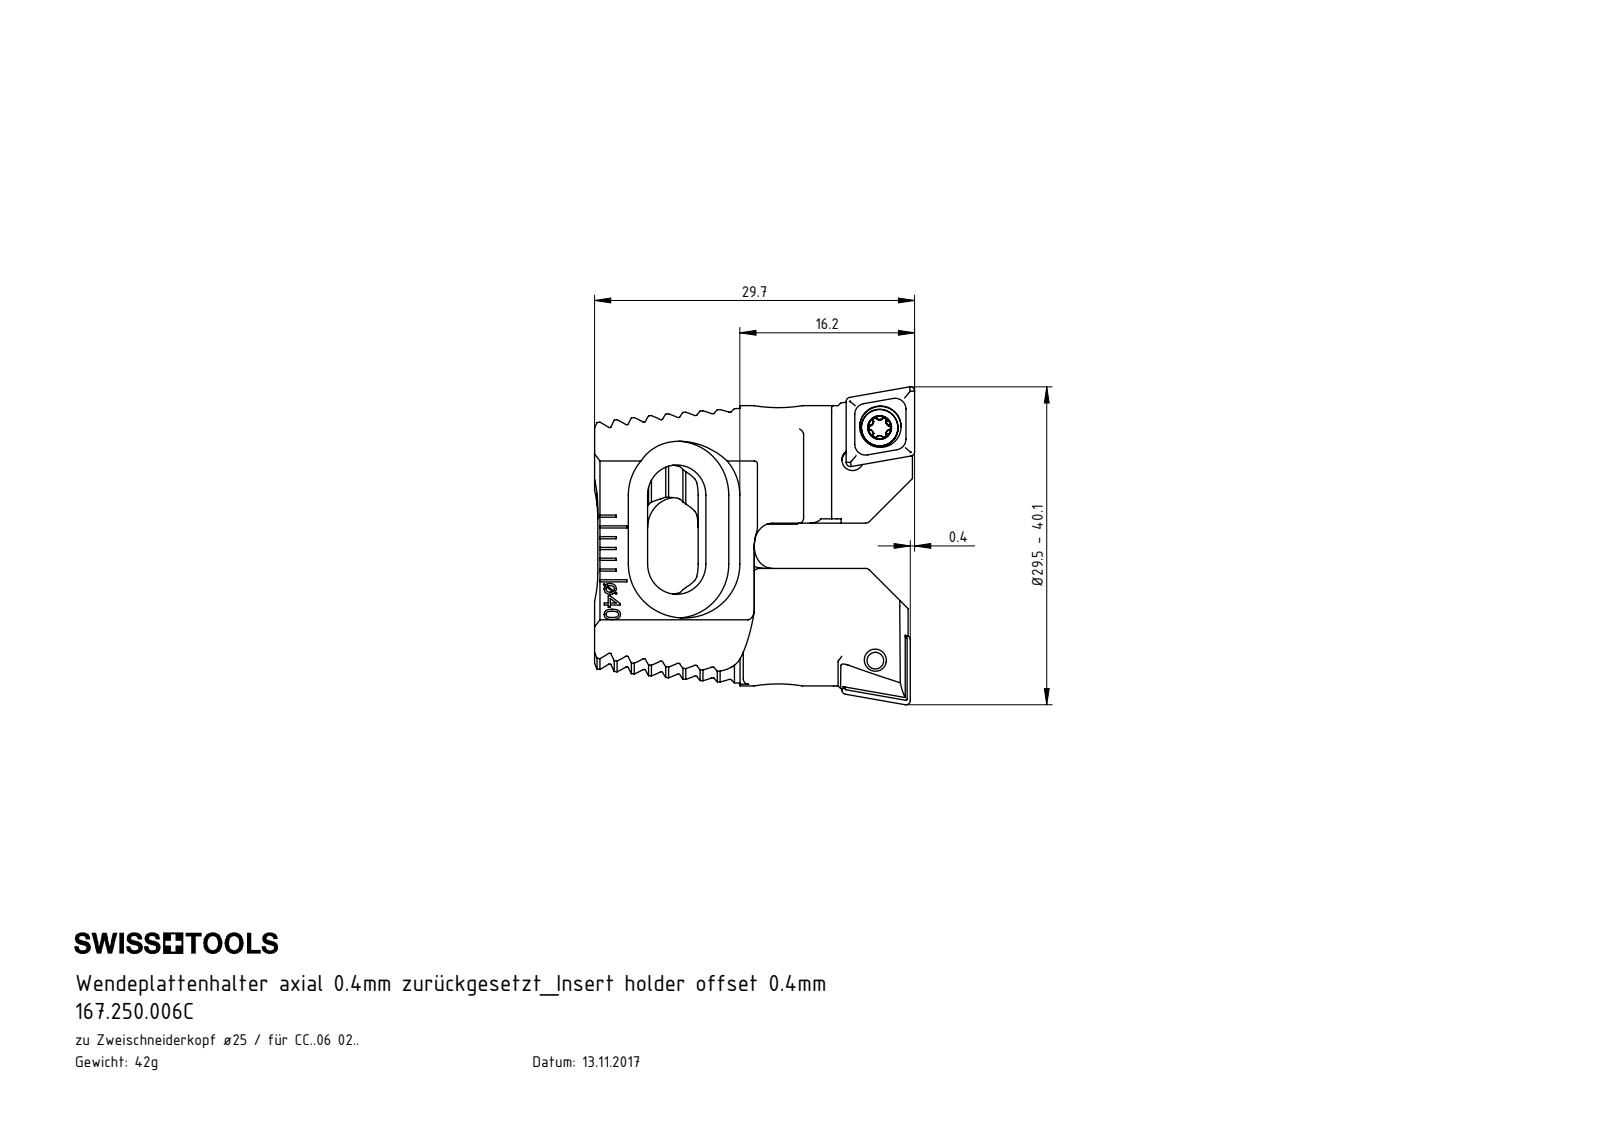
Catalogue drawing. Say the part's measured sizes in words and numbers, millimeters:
The part is named "CCMT060204; WCA-ER2.001.006_B; 167.250.006C; Z25-ER3.001.010_A (+3 more)". Its 3-D file was written by "SolidWorks 2017 (CONFIG_CONTROL_DESIGN)". It is 9 solids with 680 faces: 313 planar, 161 cylindrical and 206 other. Overall it measures 29.7 by 29.5 by 20.29 millimeters. Its volume is 5 270 cubic millimeters and its surface area 4 868 square millimeters. Round holes: 4 of diameter 1.6, 2 of diameter 2, 2 of diameter 2.05, 2 of diameter 2.8, 2 of diameter 3.85, 1 of diameter 3.5. Round bosses or shafts: 2 of diameter 3.4, 2 of diameter 2.5, 1 of diameter 4. Partial cylindrical surfaces (rounded edges, fillets, slot ends): 18 of radius 0.5, 16 of radius 0.12, 12 of radius 0.21, 10 of radius 0.36, 4 of radius 2, 4 of radius 2.8, 4 of radius 5, 4 of radius 12. The main face-to-face distances are 1.43, 2.86, 4.29, 5.72, 7.15, 3.9, 8.58, 4.6, 10, 0.4. The hole center spacings are 3.91, 4.01, 7, 21.97, 2.49, 2.51, 5, 7.43.
